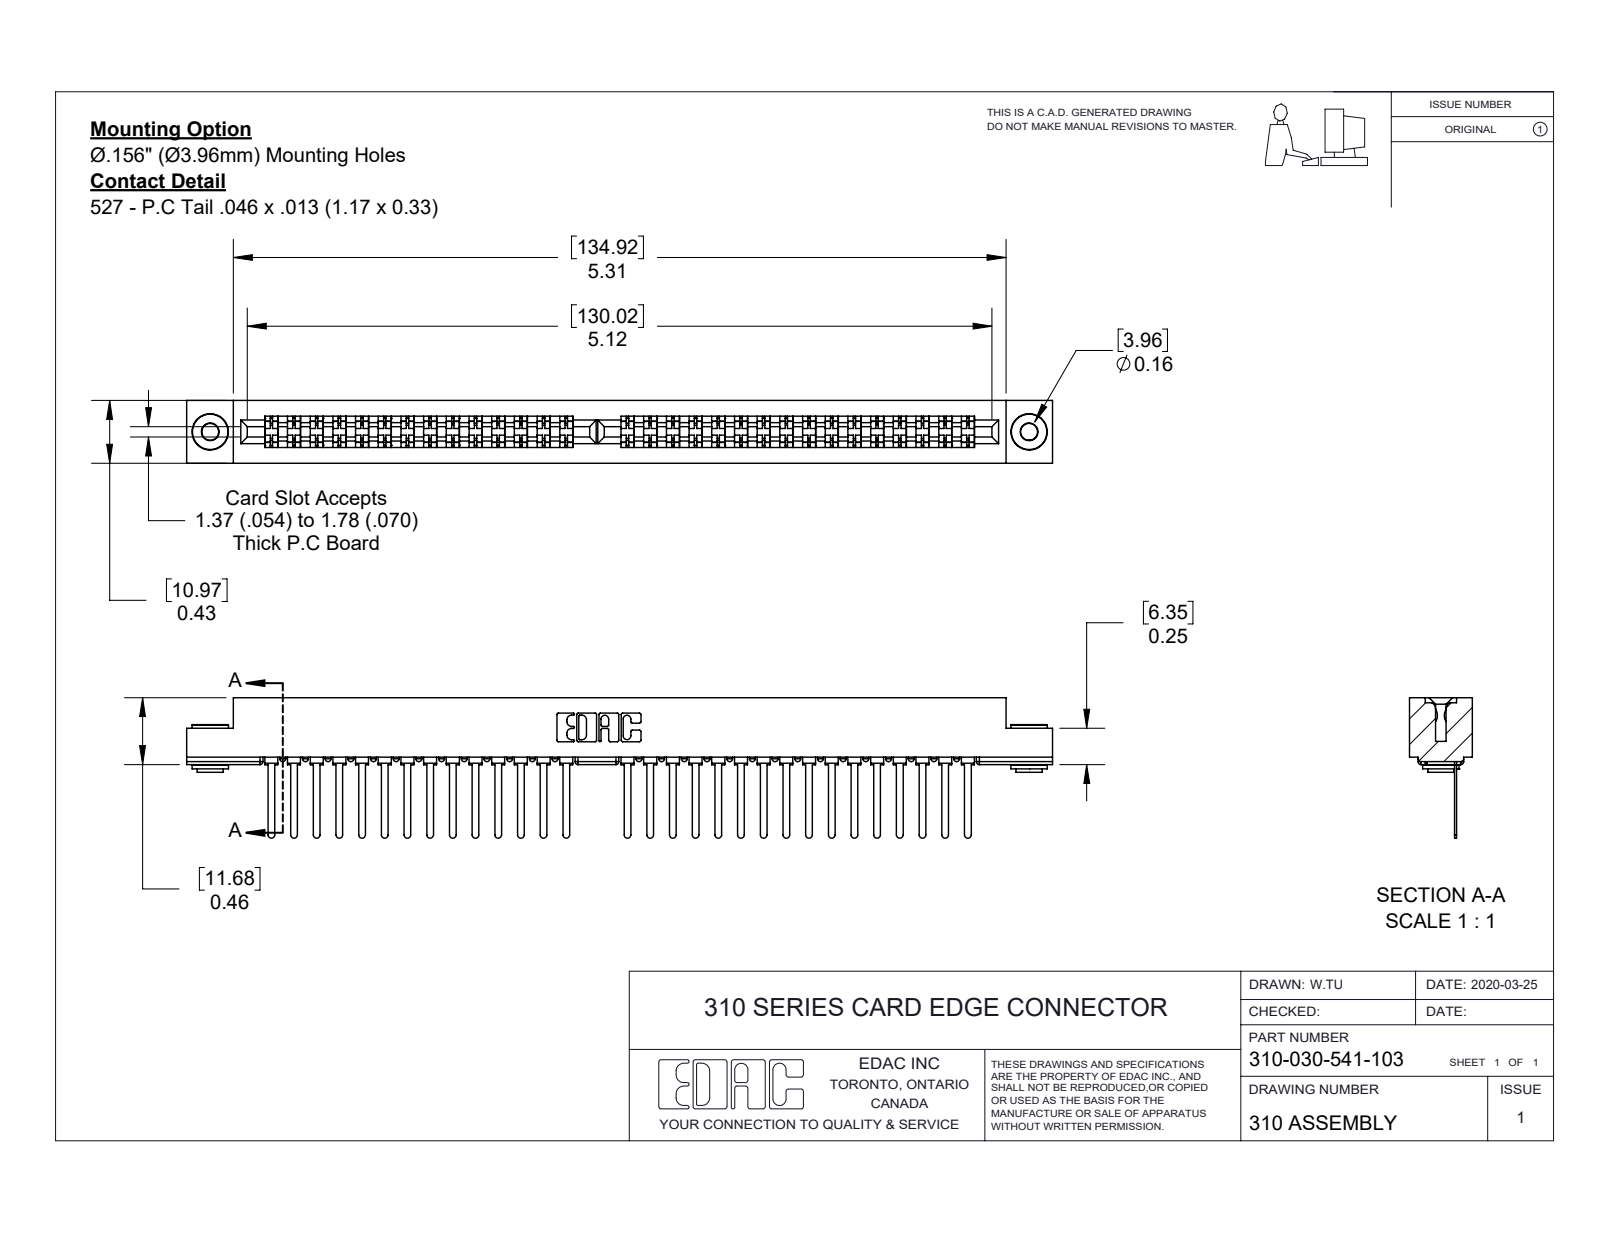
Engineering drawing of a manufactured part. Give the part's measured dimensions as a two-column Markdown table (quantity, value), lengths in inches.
| quantity | value |
| --- | --- |
| part name | 307-290-002_541; 345-250-002_345-250-002-102; 310 Part_.116 Hex; 310-030-541-103 |
| STEP written by | SolidWorks 2016 (CONFIG_CONTROL_DESIGN) |
| units | inches |
| bodies | 33 solids, 2438 faces (1458 planar, 908 cylindrical, 72 other) |
| overall size | 5.953 × 0.966 × 0.432 |
| volume | 0.805 in³ |
| surface area | 29.89 in² |
| round holes (diameter × count) | 0.116 × 2, 0.156 × 2 |
| round bosses / shafts (diameter × count) | 0.25 × 2, 0.18 × 2, 0.136 × 2 |
| partial cylindrical surfaces (radius × count) | 0.02 × 98, 0.023 × 30, 0.01 × 22, 0.007 × 6, 0.031 × 6, 0.026 × 3, 0.012 × 2, 0.025 × 2 |
| main face-to-face distances | 0.109, 0.324, 0.013, 0.122, 0.311, 0.202, 0.432, 0.215, 0.049, 0.153 |
| hole center spacings | 5.63 |
